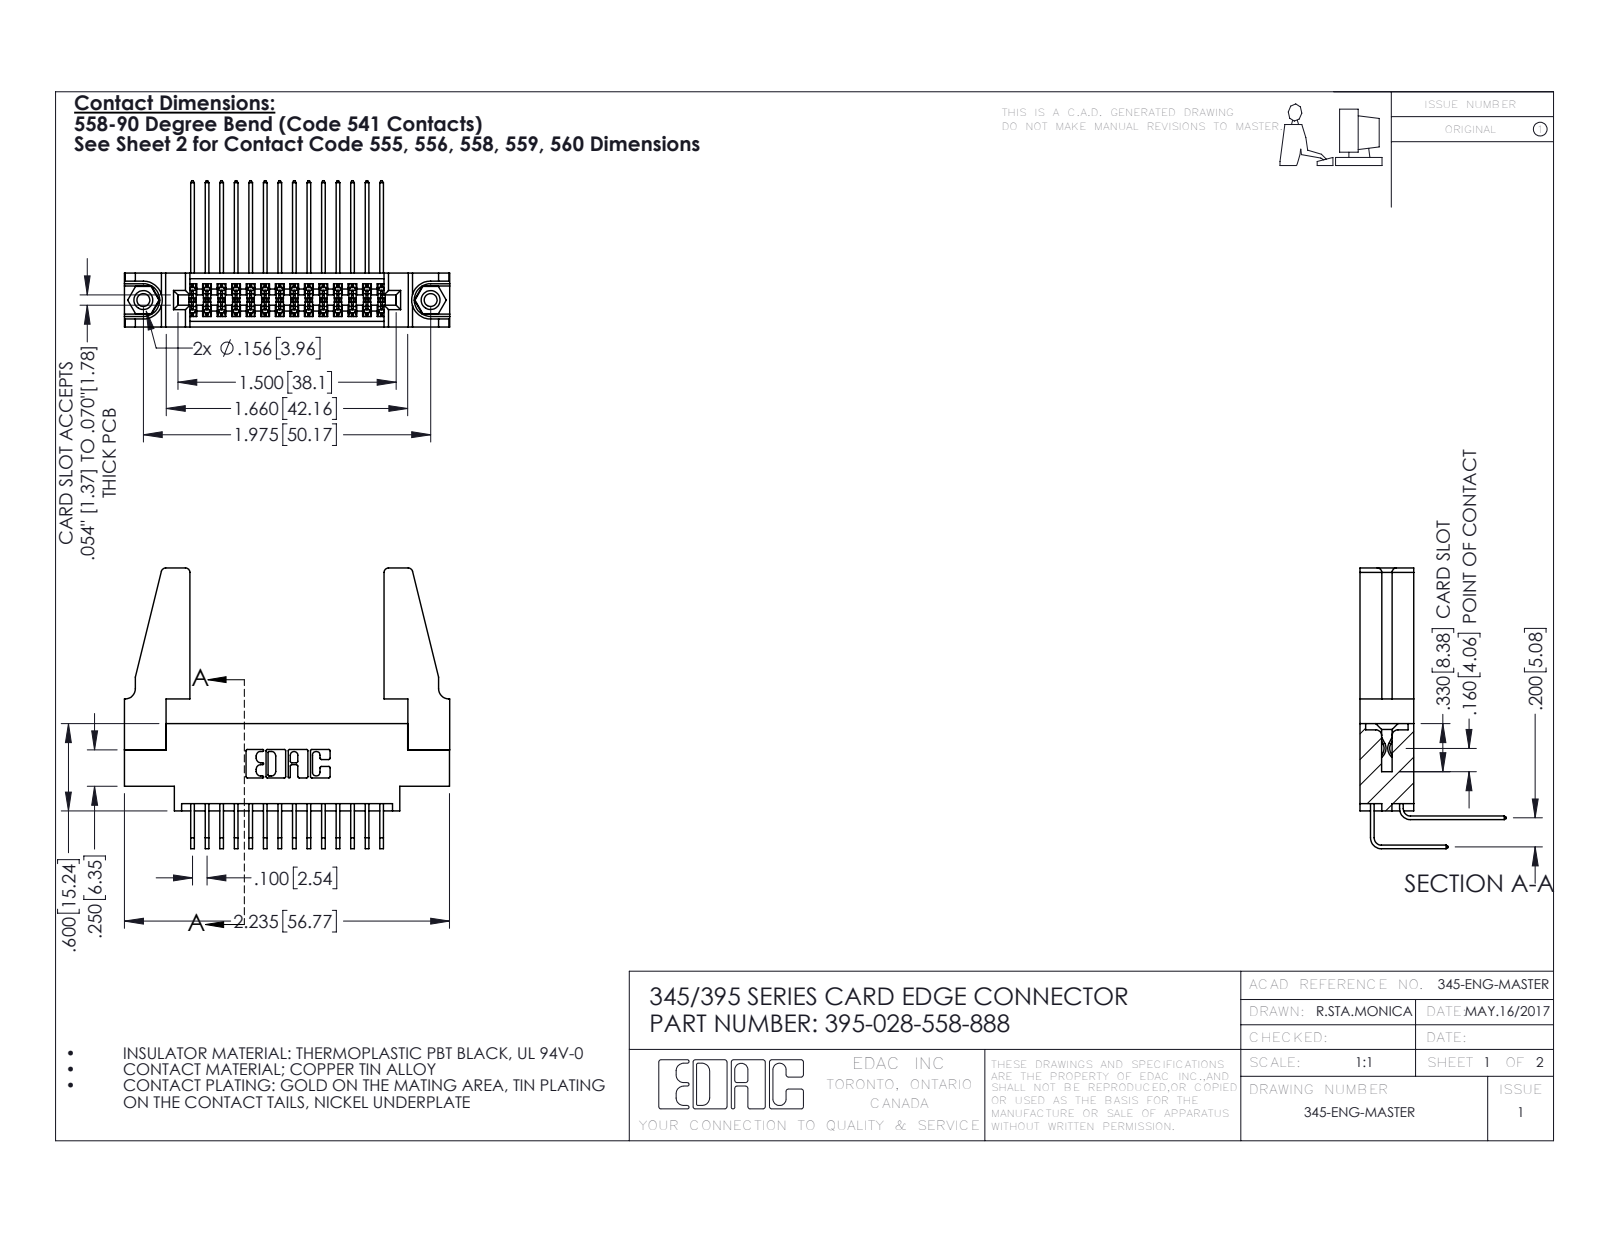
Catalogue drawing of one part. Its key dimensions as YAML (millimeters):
part_name: "395-028-558-888; 345-250-001_345-250-001-102; 345 Part_0.170 Offset - 0.156 Dia-TH; 345-220-078_345-220-088 (+2 more)"
step_written_by: "SolidWorks 2016 (CONFIG_CONTROL_DESIGN)"
units: millimeters
bodies: {solids: 33, faces: 1710, planar: 1136, cylindrical: 558, other: 16}
overall_size: [56.8, 49, 25.5]
volume: 8550
surface_area: 11320
round_holes:
  - {diameter: 2.3, count: 2}
  - {diameter: 3.2, count: 2}
  - {diameter: 4, count: 2}
  - {diameter: 1.6, count: 1}
round_bosses_or_shafts:
  - {diameter: 3.9, count: 2}
partial_cylinders:
  - {radius: 0.2, count: 43}
  - {radius: 0.3, count: 22}
  - {radius: 0.8, count: 8}
  - {radius: 0.2, count: 6}
  - {radius: 0.8, count: 6}
  - {radius: 0.7, count: 3}
  - {radius: 0.4, count: 2}
  - {radius: 0.5, count: 2}
face_to_face_distances: [9.4, 1.8, 7.6, 5.1, 2.5, 6.9, 0.6, 5.7, 4.4, 3.8]
hole_center_spacings: [6.9, 44.2, 50.2]
